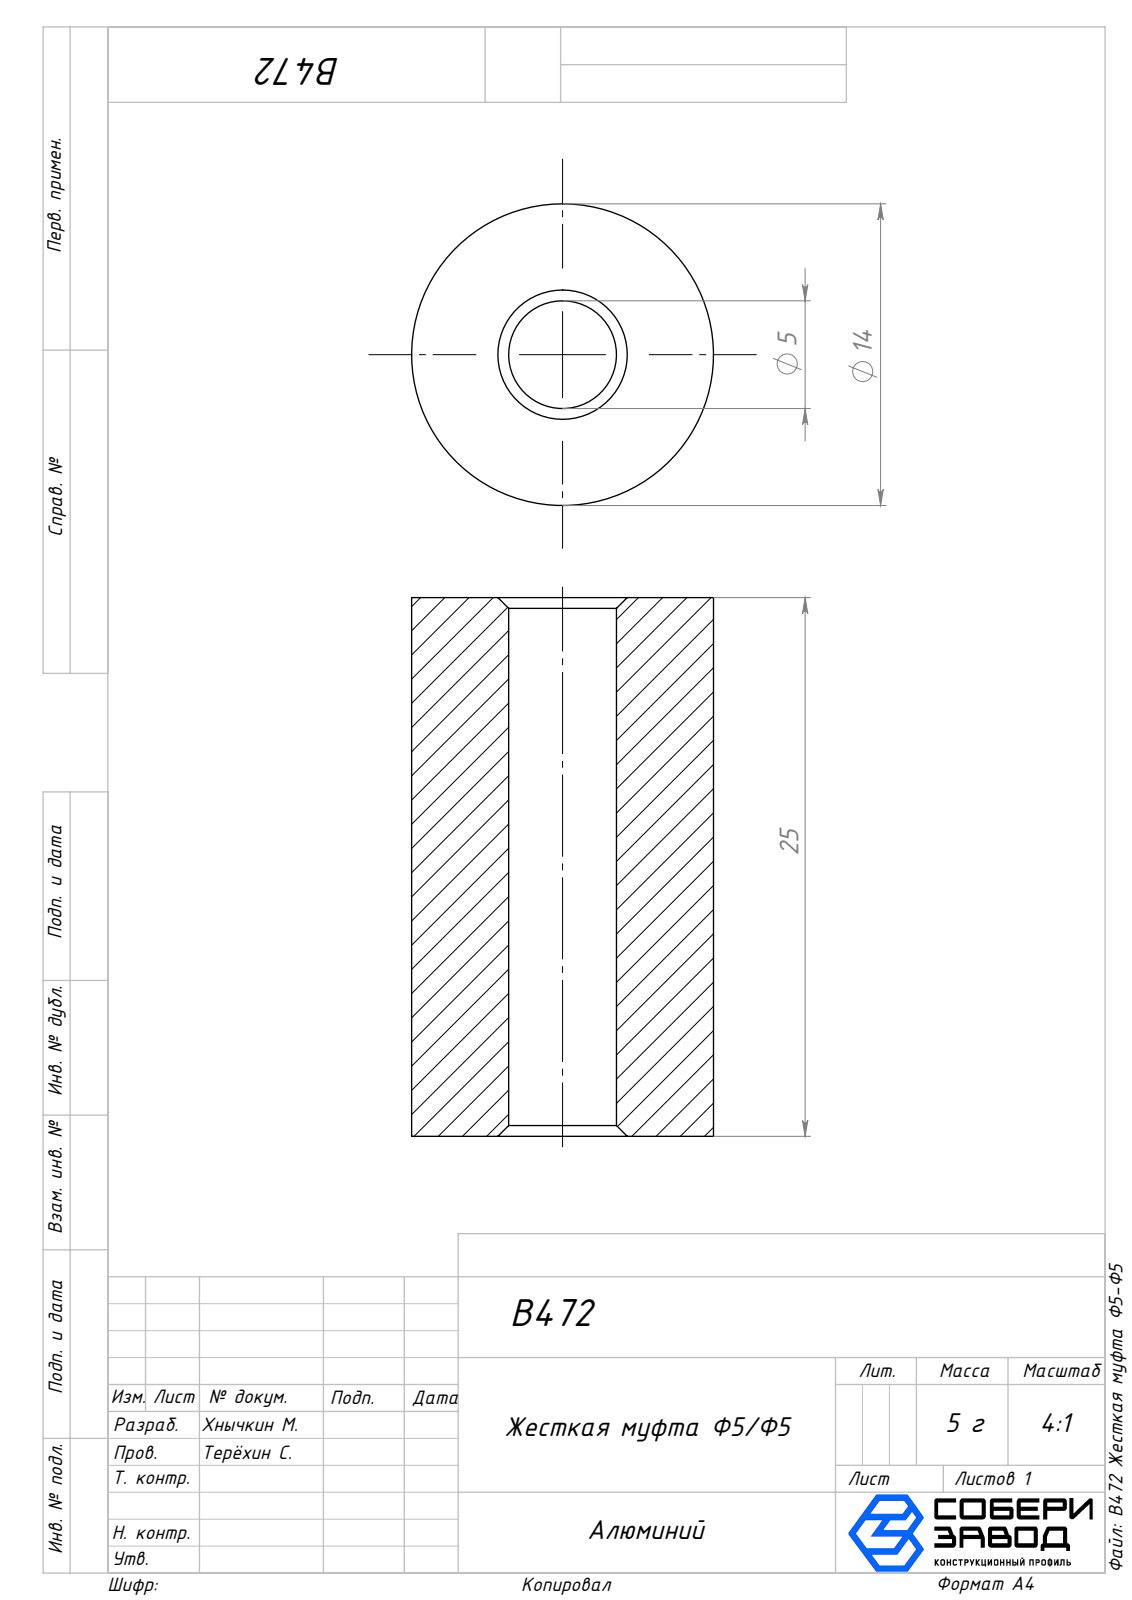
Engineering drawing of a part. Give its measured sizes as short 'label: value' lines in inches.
name: B472 Жесткая муфта Ф5-Ф5
written by: SolidWorks 2025 (AUTOMOTIVE_DESIGN)
unit: in
bodies: 1 solid, 10 faces (2 planar, 4 cylindrical, 4 other)
size: 0.984 × 0.551 × 0.551
volume: 0.205 in³; area: 2.716 in²
holes: 1× ⌀0.197
bosses: 1× ⌀0.551
face distances: 0.984
